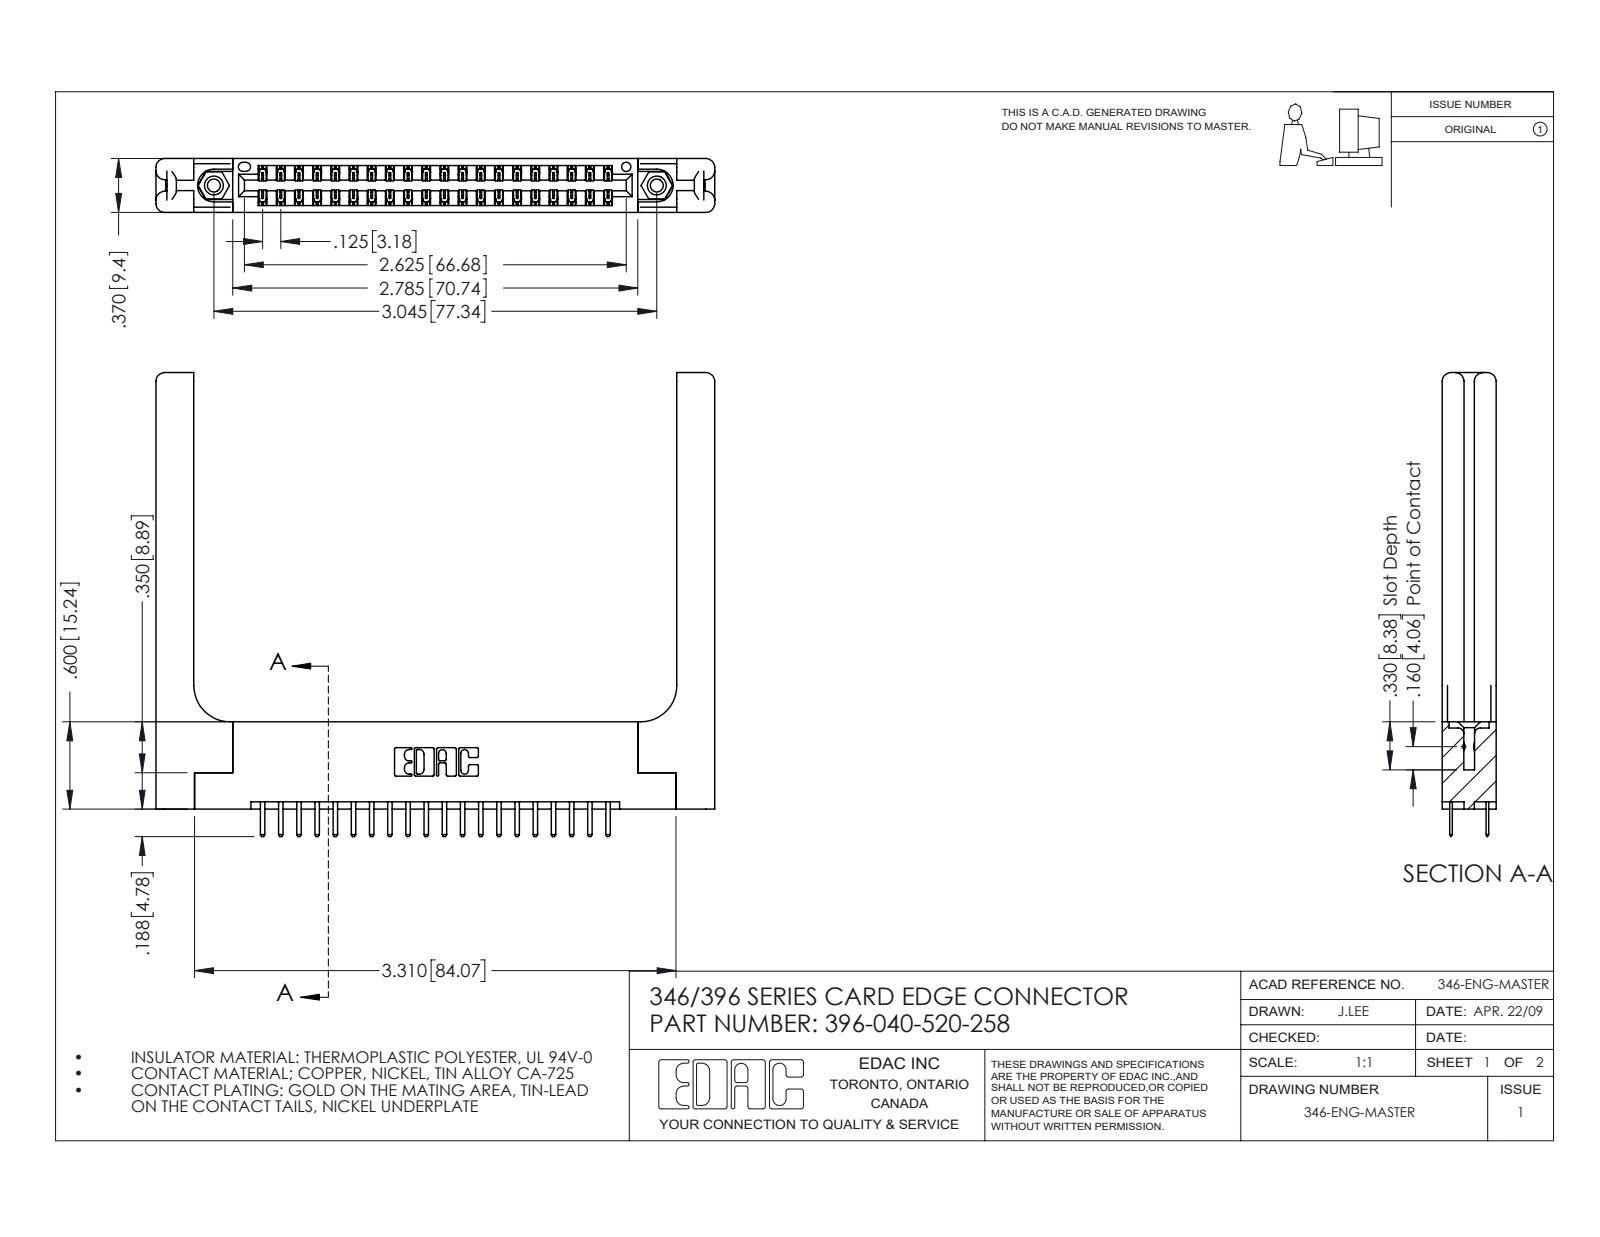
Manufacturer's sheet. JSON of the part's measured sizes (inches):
{"part_name": "345-292-001_345-293-120; 346 Part_Flush Mounting Lugs - 0.156 Dia-TH; 346-220-058_345-220-058; 396-040-520-258 (+1 more)", "step_written_by": "SolidWorks 2016 (CONFIG_CONTROL_DESIGN)", "units": "inches", "bodies": {"solids": 45, "faces": 2618, "planar": 1704, "cylindrical": 854, "other": 60}, "overall_size": [3.841, 3.188, 0.37], "volume_in3": 1.026, "surface_area_in2": 26.98, "round_holes": [[0.089, 2], [0.125, 2], [0.156, 2], [0.064, 1]], "round_bosses_or_shafts": [[0.155, 2]], "partial_cylinders_radius": [[0.006, 60], [0.01, 44], [0.01, 22], [0.06, 16], [0.007, 6], [0.031, 6], [0.026, 3], [0.014, 2]], "face_to_face_distances": [0.37, 0.072, 0.15, 0.148, 0.048, 0.322, 0.25, 0.077, 0.102, 0.22], "hole_center_spacings": [0.246, 2.837, 3.045]}
